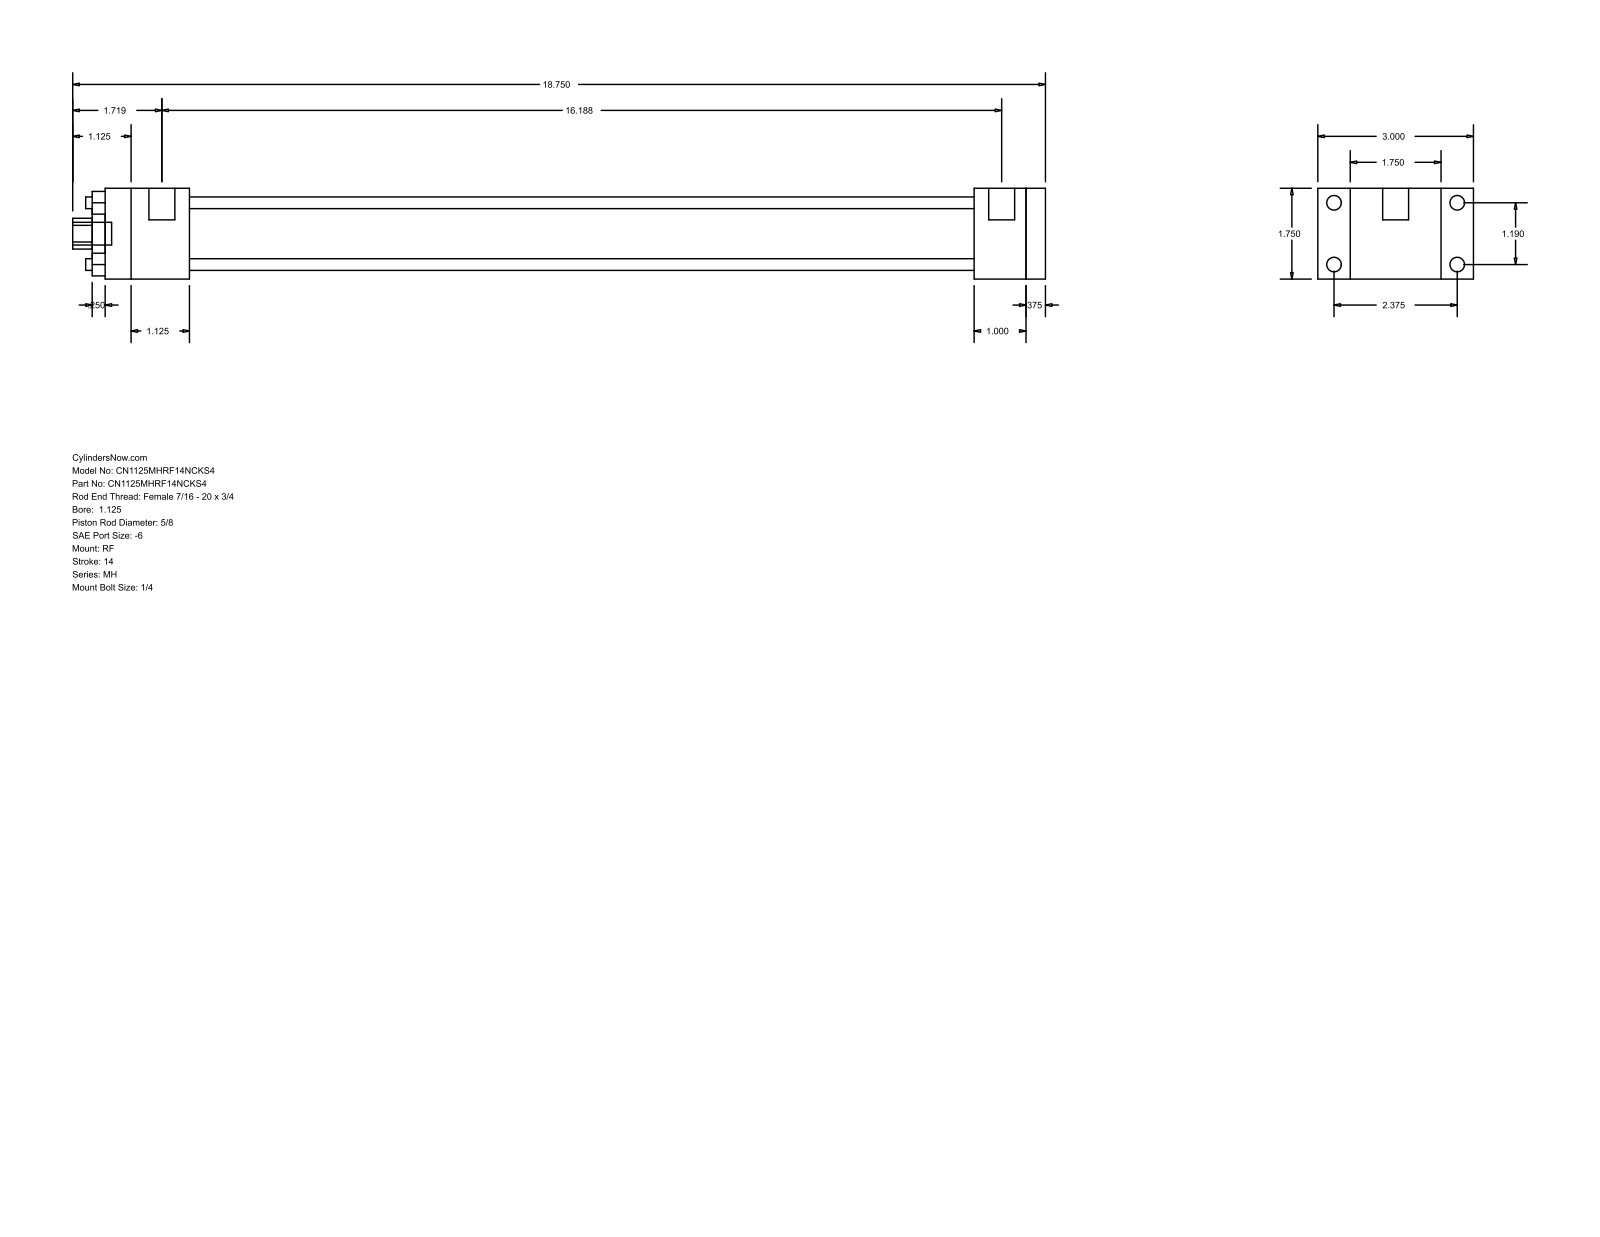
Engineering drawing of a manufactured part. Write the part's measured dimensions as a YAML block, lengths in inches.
part_name: "MH_RF__0112_0.625"
step_written_by: "GSSL Pune (CONFIG_CONTROL_DESIGN)"
units: inches
bodies: {solids: 0, faces: 92, planar: 64, cylindrical: 28, other: 0}
overall_size: [18.75, 3, 1.75]
round_holes:
  - {diameter: 0.225, count: 4}
  - {diameter: 0.625, count: 1}
  - {diameter: 1.125, count: 1}
  - {diameter: 1.375, count: 1}
round_bosses_or_shafts:
  - {diameter: 0.281, count: 4}
  - {diameter: 0.219, count: 4}
  - {diameter: 0.5, count: 2}
  - {diameter: 0.437, count: 1}
partial_cylinders:
  - {radius: 0.297, count: 1}
face_to_face_distances: [1.75, 0.375, 0.625, 16.125, 16.5, 15.125, 1, 1.375, 1.625, 16.75]
hole_center_spacings: [0.841, 1.19, 1.683]
